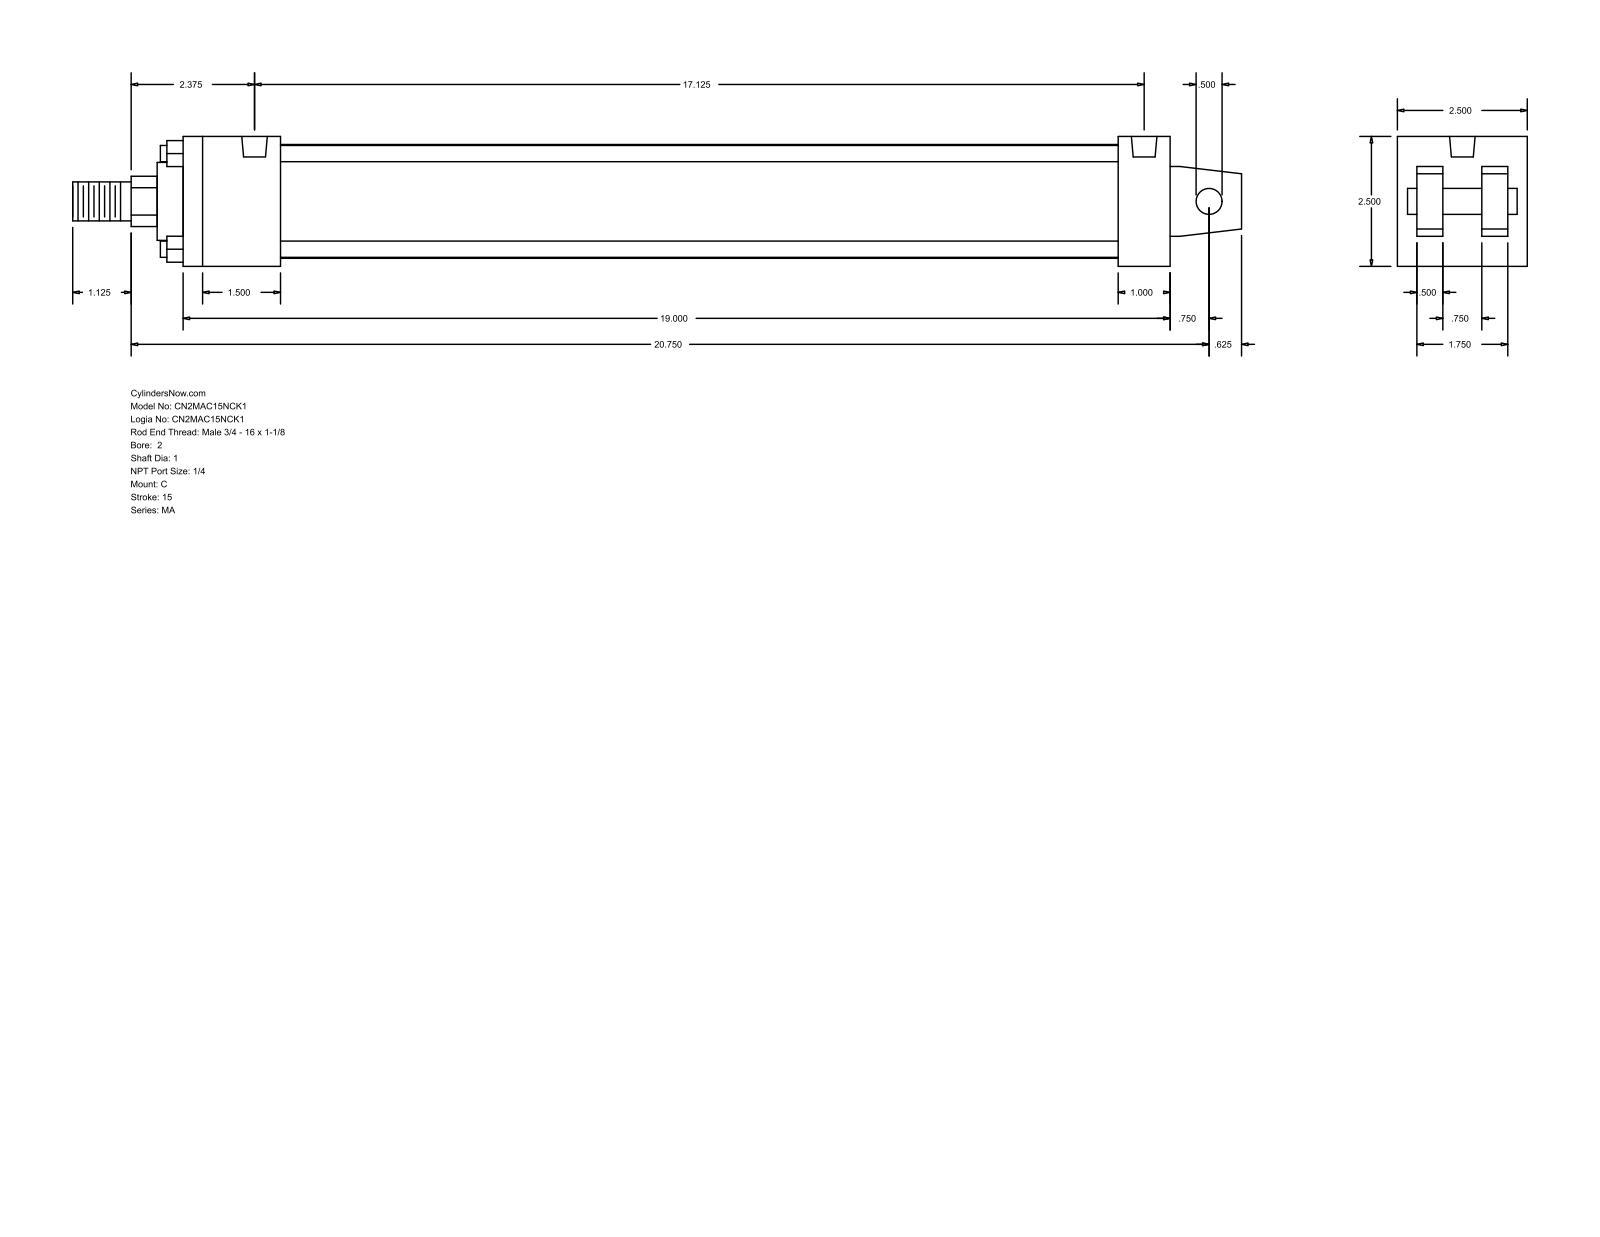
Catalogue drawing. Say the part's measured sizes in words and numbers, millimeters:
The part is named "MA_C__0200_1". Its 3-D file was written by "GSSL Pune (CONFIG_CONTROL_DESIGN)". It is 0 solids with 103 faces: 76 planar, 27 cylindrical and 0 other. Overall it measures 571.5 by 63.5 by 63.5 millimeters. Round holes: 4 of diameter 7.94, 2 of diameter 12.49. Round bosses or shafts: 4 of diameter 7.94, 1 of diameter 55.63, 1 of diameter 38.1, 1 of diameter 25.4, 1 of diameter 19.05, 1 of diameter 12.7. Partial cylindrical surfaces (rounded edges, fillets, slot ends): 1 of radius 12.29. The main face-to-face distances are 63.5, 12.7, 482.6, 22.22, 41.28, 9.52, 53.98, 31.76, 47.63, 25.4. The hole center spacings are 434.97.
